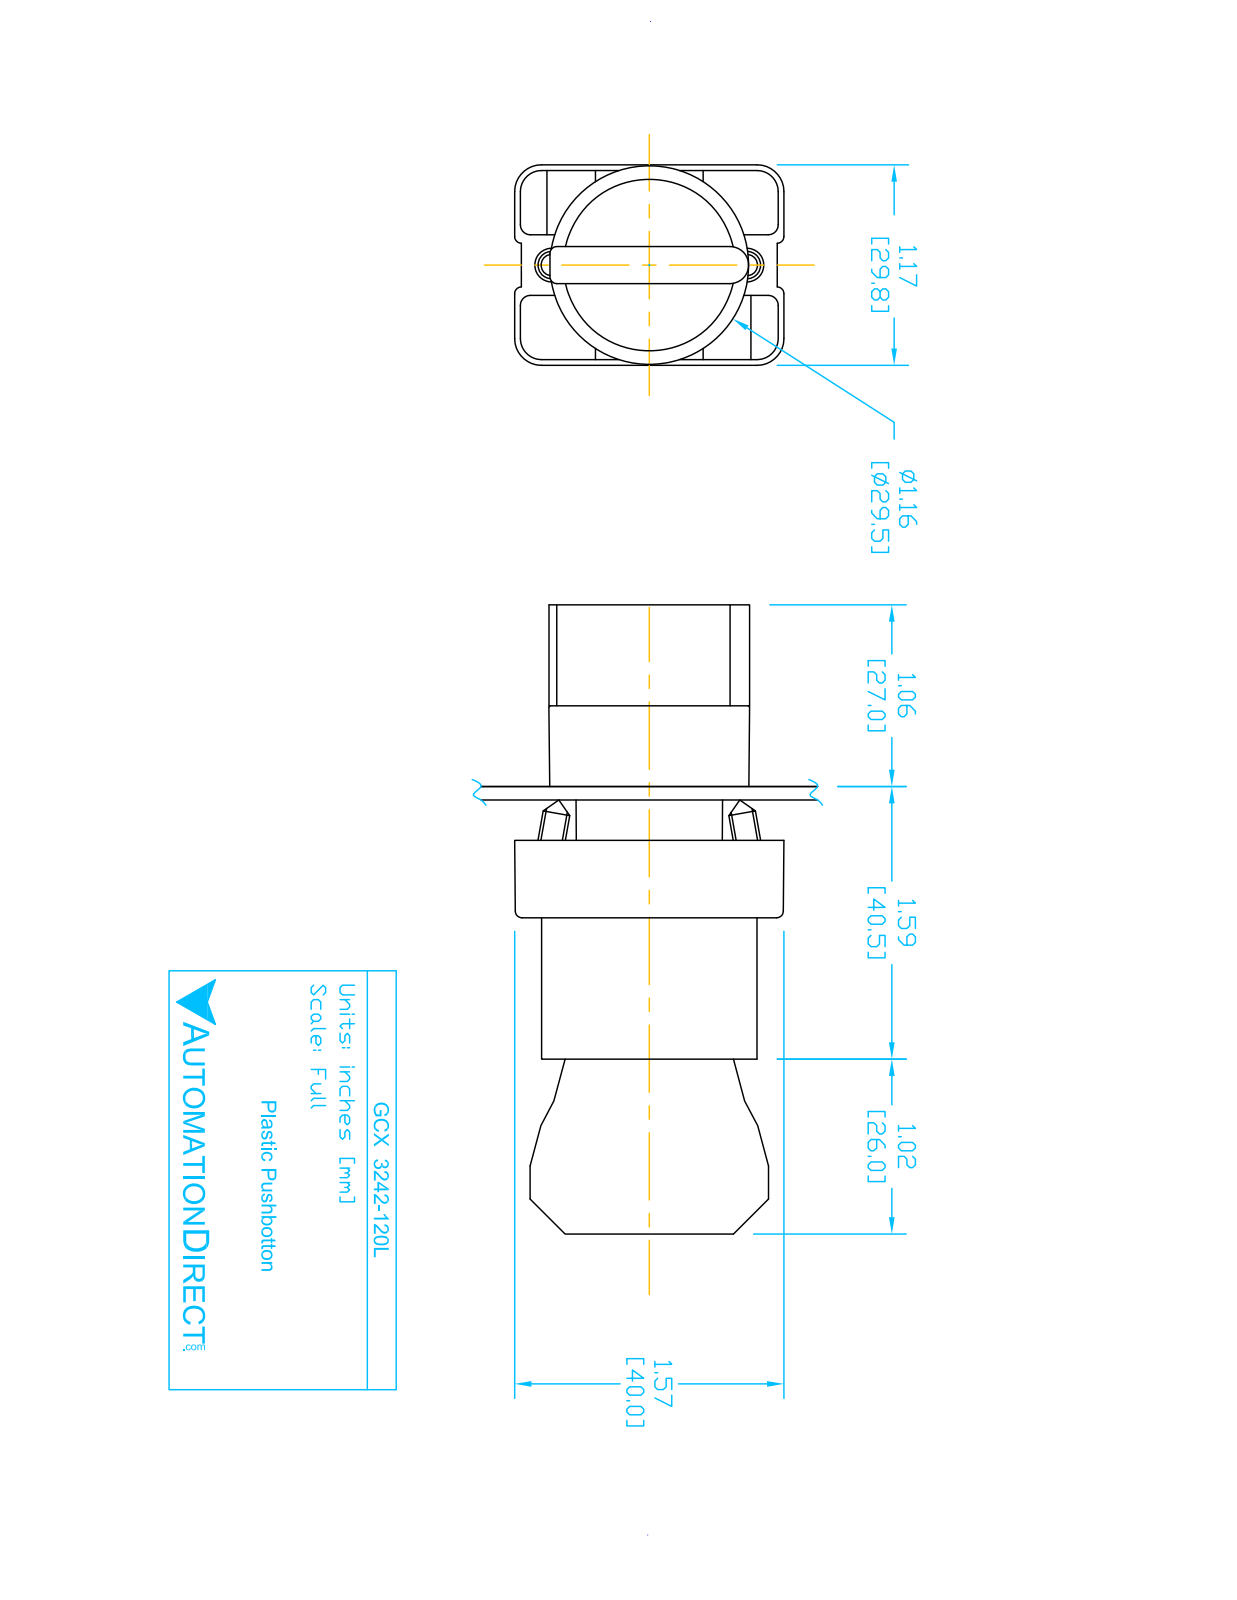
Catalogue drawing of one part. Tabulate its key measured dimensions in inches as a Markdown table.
| quantity | value |
| --- | --- |
| part name | ECX1050; GCX3242-120L; ecx1040; GCX3242L OPERATOR (+1 more) |
| STEP written by | SolidWorks 2016 (AUTOMOTIVE_DESIGN) |
| units | inches |
| bodies | 8 solids, 445 faces (263 planar, 151 cylindrical, 31 other) |
| overall size | 3.653 × 1.581 × 1.177 |
| volume | 2.799 in³ |
| surface area | 39 in² |
| round holes (diameter × count) | 0.079 × 2, 0.124 × 2, 0.13 × 2, 0.087 × 1, 0.197 × 1, 0.469 × 1, 0.878 × 1, 0.888 × 1, 1.024 × 1 |
| round bosses / shafts (diameter × count) | 0.157 × 4, 1.175 × 1, 1.004 × 1, 0.945 × 1, 0.856 × 1, 0.78 × 1, 0.504 × 1 |
| partial cylindrical surfaces (radius × count) | 0.059 × 24, 0.041 × 12, 0.124 × 12, 0.157 × 12, 0.039 × 9, 0.128 × 2, 0.02 × 1, 0.063 × 1 |
| main face-to-face distances | 0.827, 2.02, 1.193, 0.579, 1.244, 1.171, 0.472, 0.469, 0.031, 0.033 |
| hole center spacings | 0.236, 0.544, 0.472, 0.49 |
